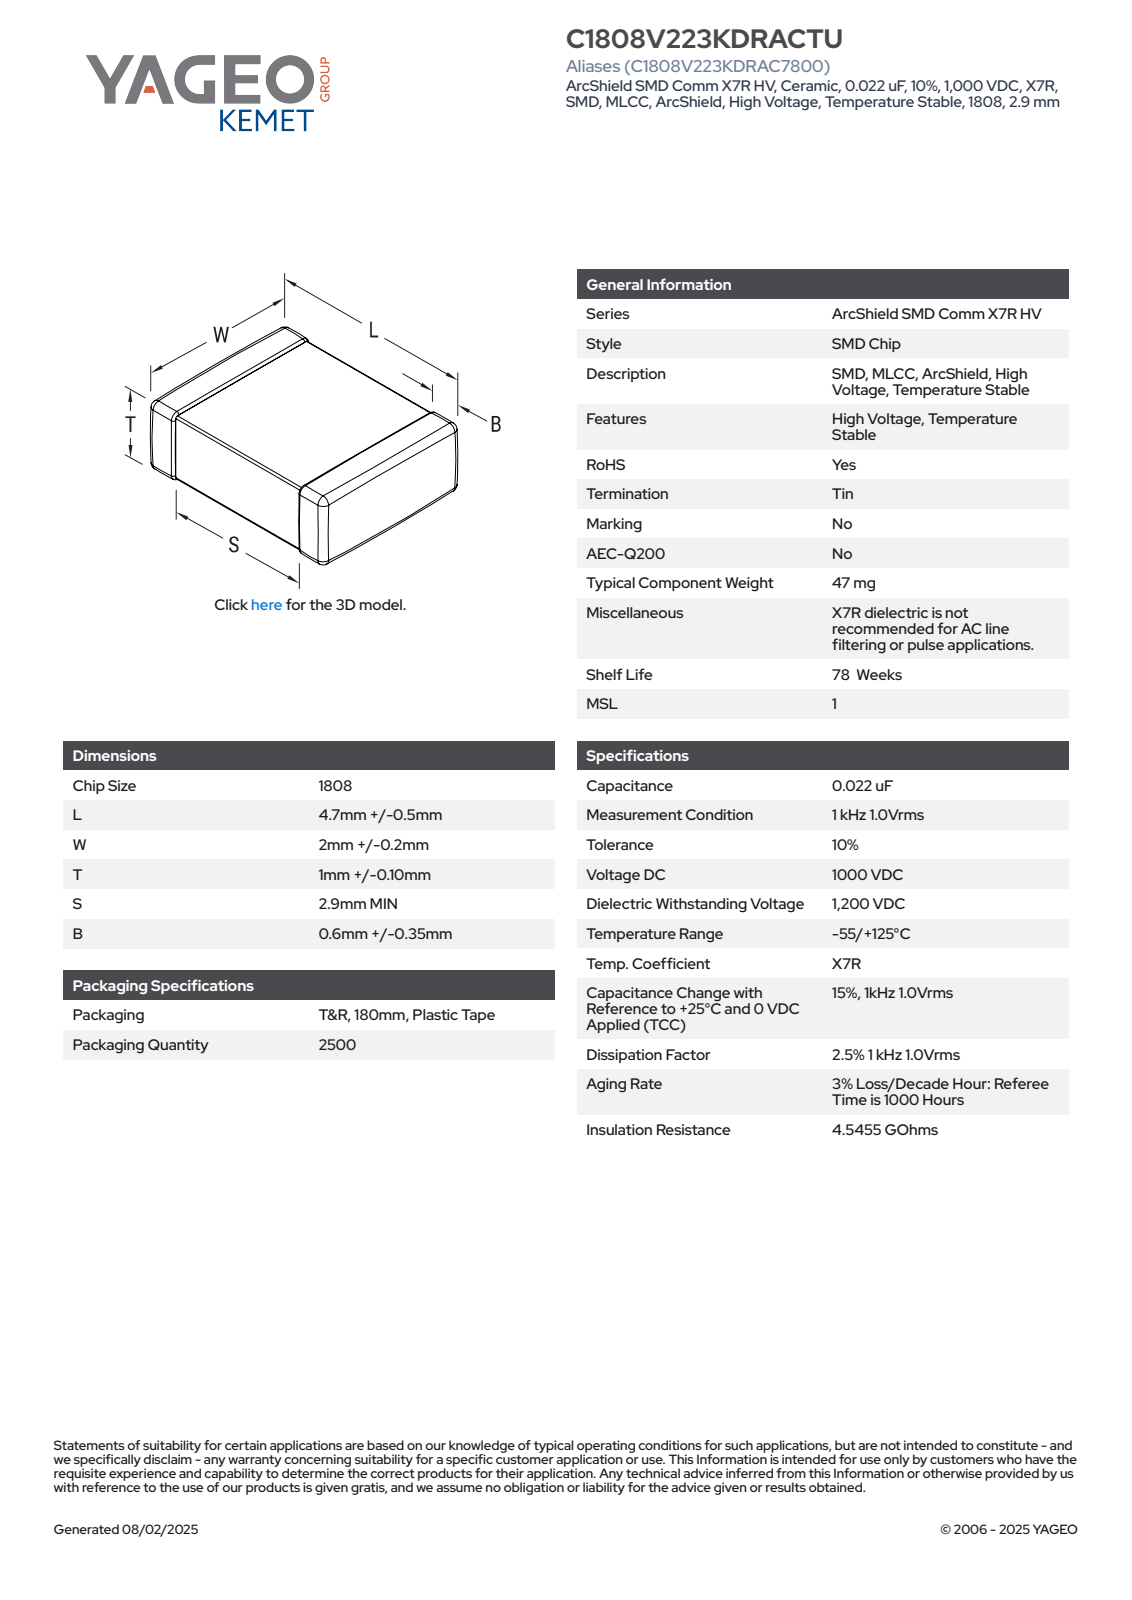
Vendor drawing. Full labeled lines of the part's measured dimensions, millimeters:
Part name (STEP PRODUCT): CCS_CCSTDNOS_1808_L5.2W2.2T1.1B0.95
STEP written by: SolidWorks 2014 (AUTOMOTIVE_DESIGN)
Units: millimetres
Bodies: 4 solids, 125 faces (71 planar, 38 cylindrical, 16 other)
Overall size (bounding box): 5.2 × 2.2 × 1.1
Volume: 12 mm³ · Surface area: 38 mm²
Main face-to-face distances: 1.05, 1, 1.1, 2.15, 2.1, 5.2, 2.2, 1.01, 1.06, 0.89
